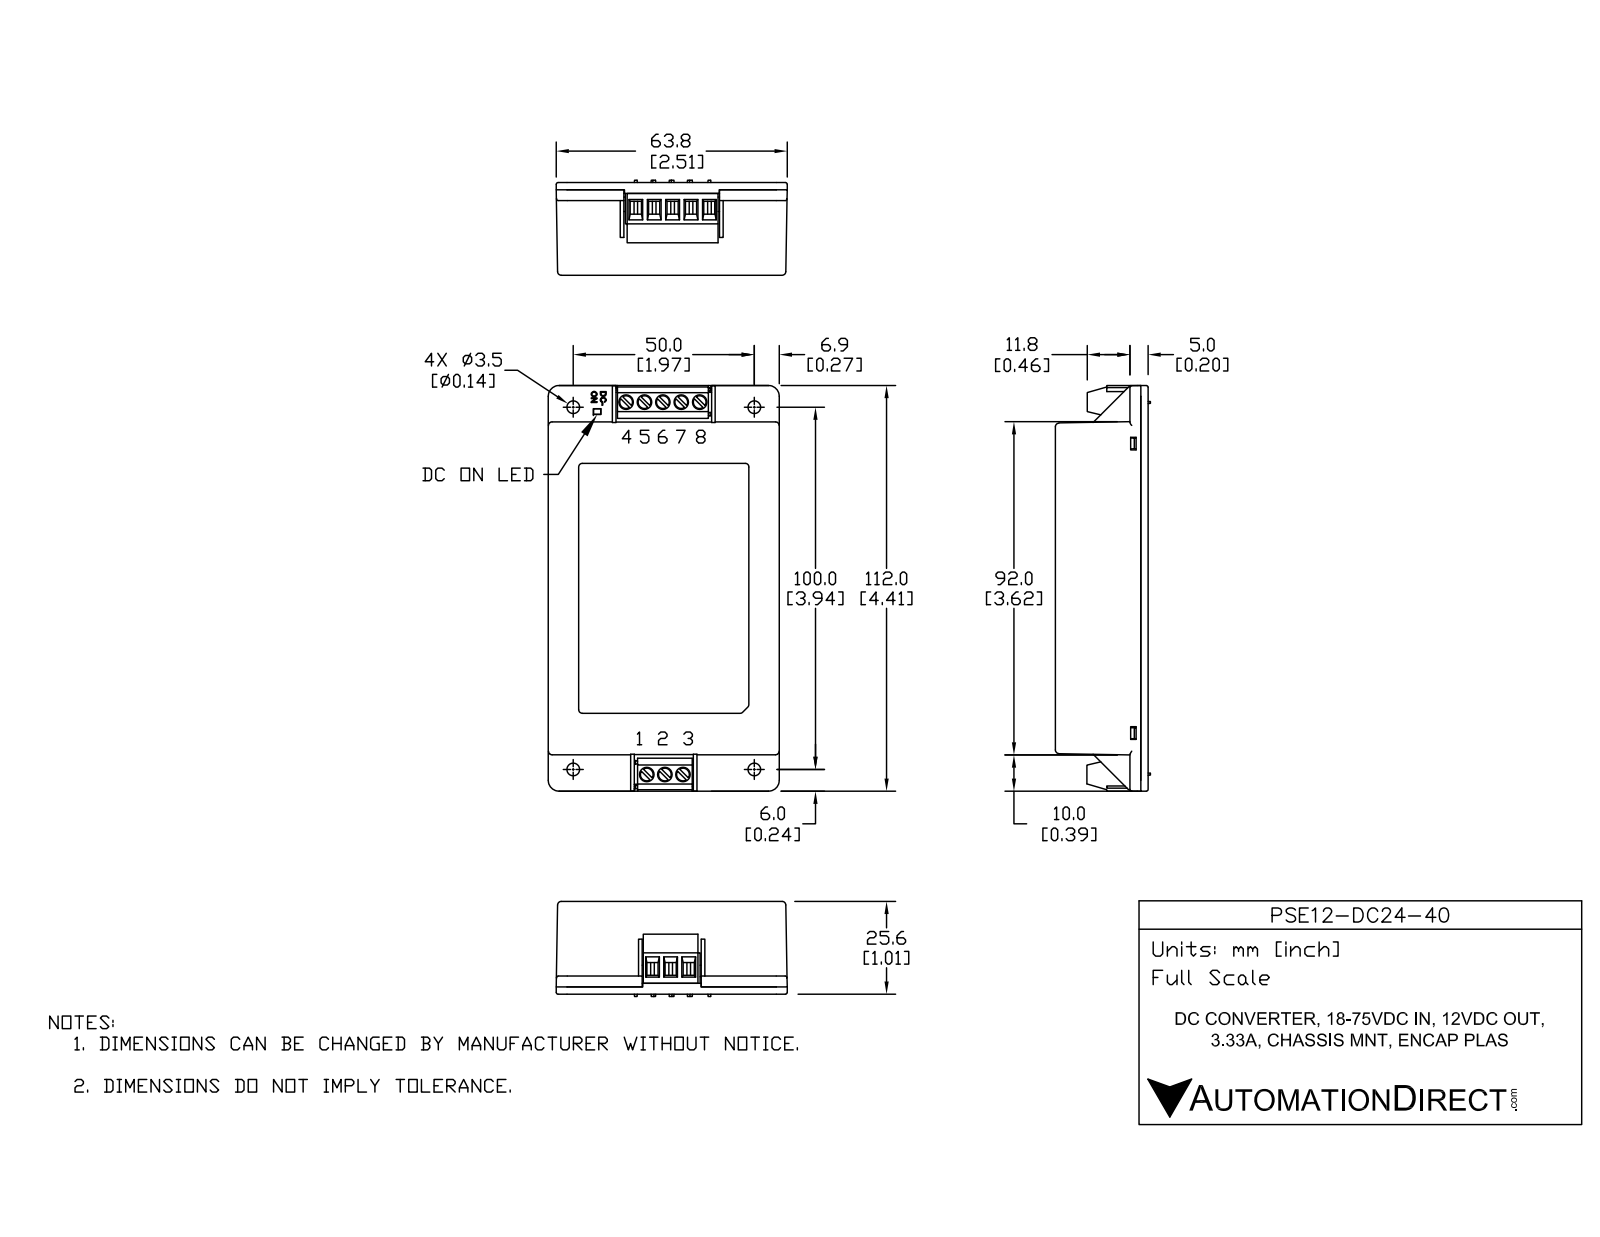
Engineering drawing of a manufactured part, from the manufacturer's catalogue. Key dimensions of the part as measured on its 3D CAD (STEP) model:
Part name (STEP PRODUCT): PSE12-DC24-40
STEP written by: SolidWorks 2019 (AUTOMOTIVE_DESIGN)
Units: millimetres
Bodies: 12 solids, 282 faces (222 planar, 54 cylindrical, 6 other)
Overall size (bounding box): 112 × 63.8 × 25.6
Volume: 158 166 mm³ · Surface area: 40 616 mm²
Round holes (diameter × count): ⌀4 ×8, ⌀3.5 ×4
Round bosses / shafts (diameter × count): ⌀3.5 ×8
Partial cylindrical surfaces — rounded edges, fillets, slot ends (radius × count): R3 ×4, R1.5 ×2
Main face-to-face distances: 2, 25.6, 23.6, 63.8, 3, 91.2, 1, 5, 20.6, 22.6
Hole centre spacings: 5.08, 10.16, 102.8, 102.9, 5, 15.24, 50, 99.9
